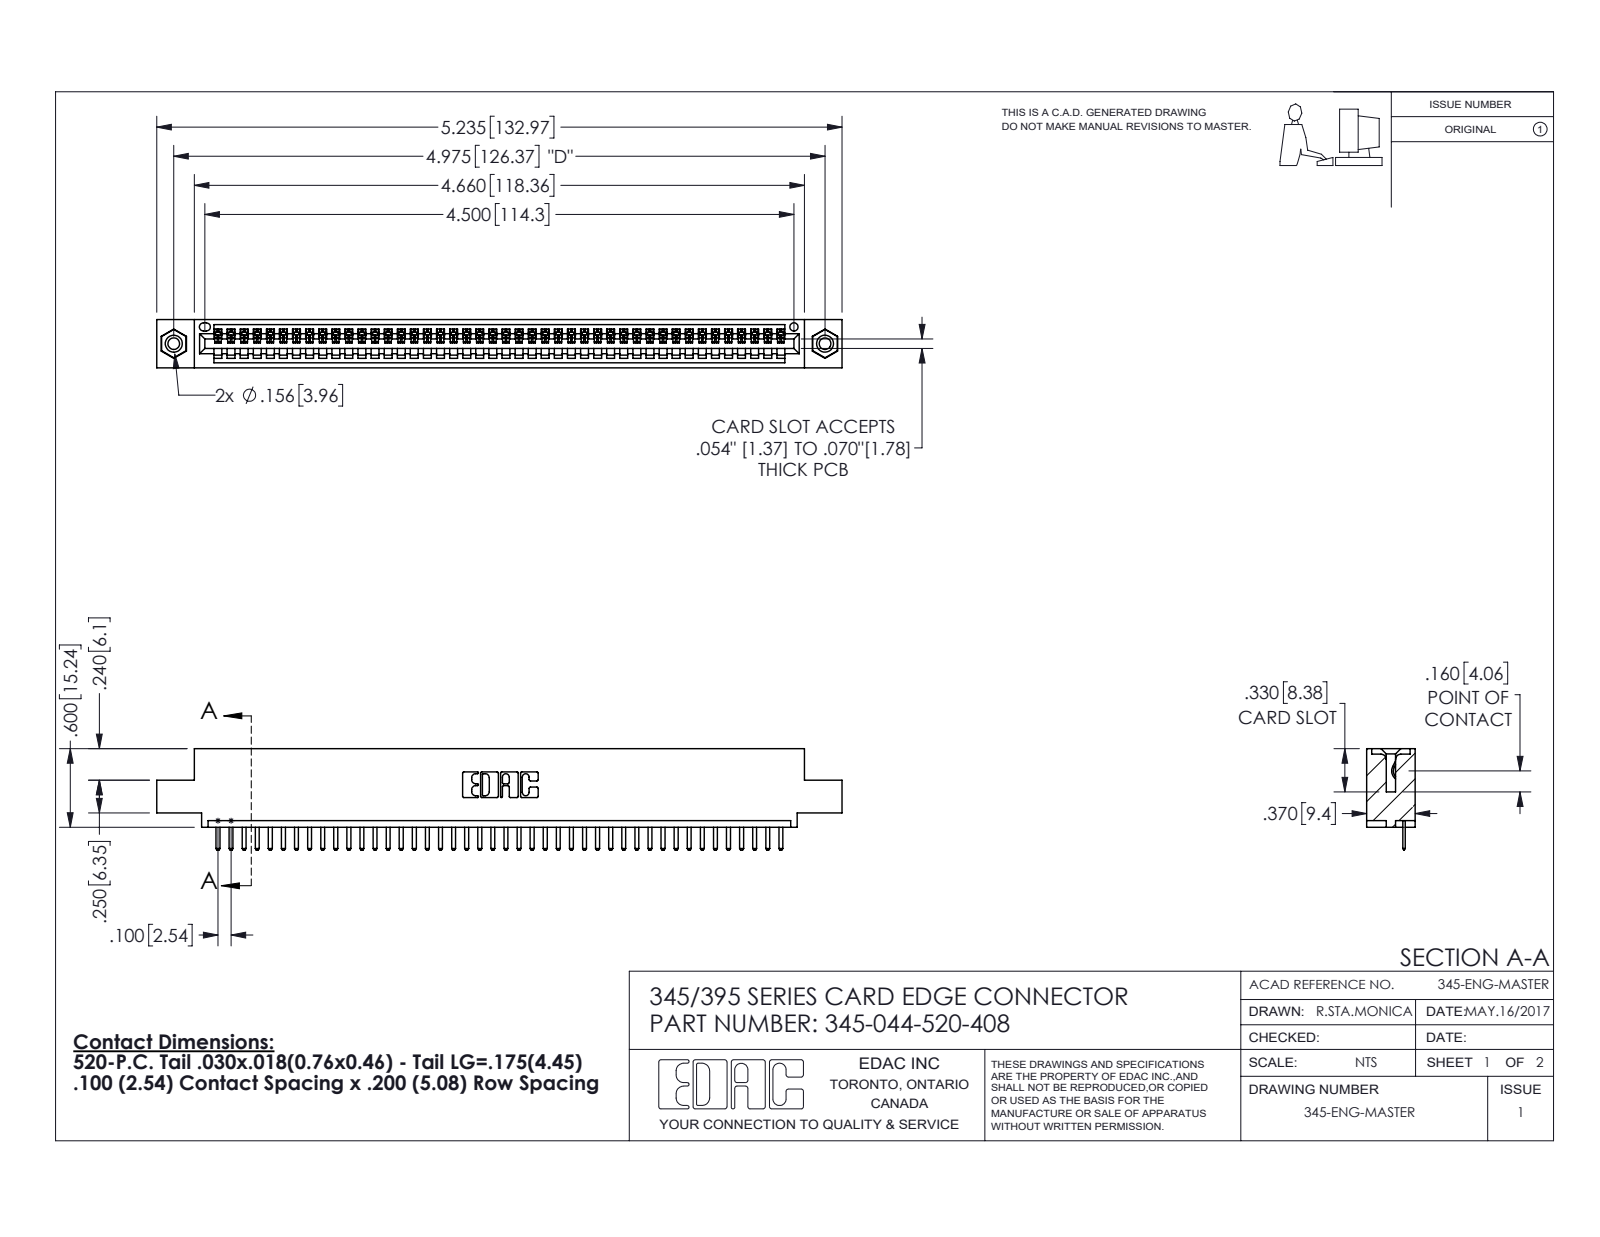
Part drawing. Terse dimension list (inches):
name: 345-292-001_345-293-120; 345-250-001_345-250-003-102; 345 Part_0.110 Offset - 0.156 Dia-TI; 345-044-520-408
written by: SolidWorks 2016 (CONFIG_CONTROL_DESIGN)
unit: in
bodies: 47 solids, 2918 faces (1964 planar, 938 cylindrical, 16 other)
size: 5.235 × 0.775 × 0.37
volume: 0.759 in³; area: 25.18 in²
holes: 2× ⌀0.089, 2× ⌀0.125, 2× ⌀0.156, 1× ⌀0.064
bosses: 2× ⌀0.155
rounds: 90× R0.01, 88× R0.006, 22× R0.01, 6× R0.007, 6× R0.031, 3× R0.026, 2× R0.031, 2× R0.04
face distances: 0.072, 0.298, 0.37, 0.2, 0.098, 0.272, 0.025, 0.225, 0.072, 0.149
hole spacings: 0.27, 4.739, 4.975
